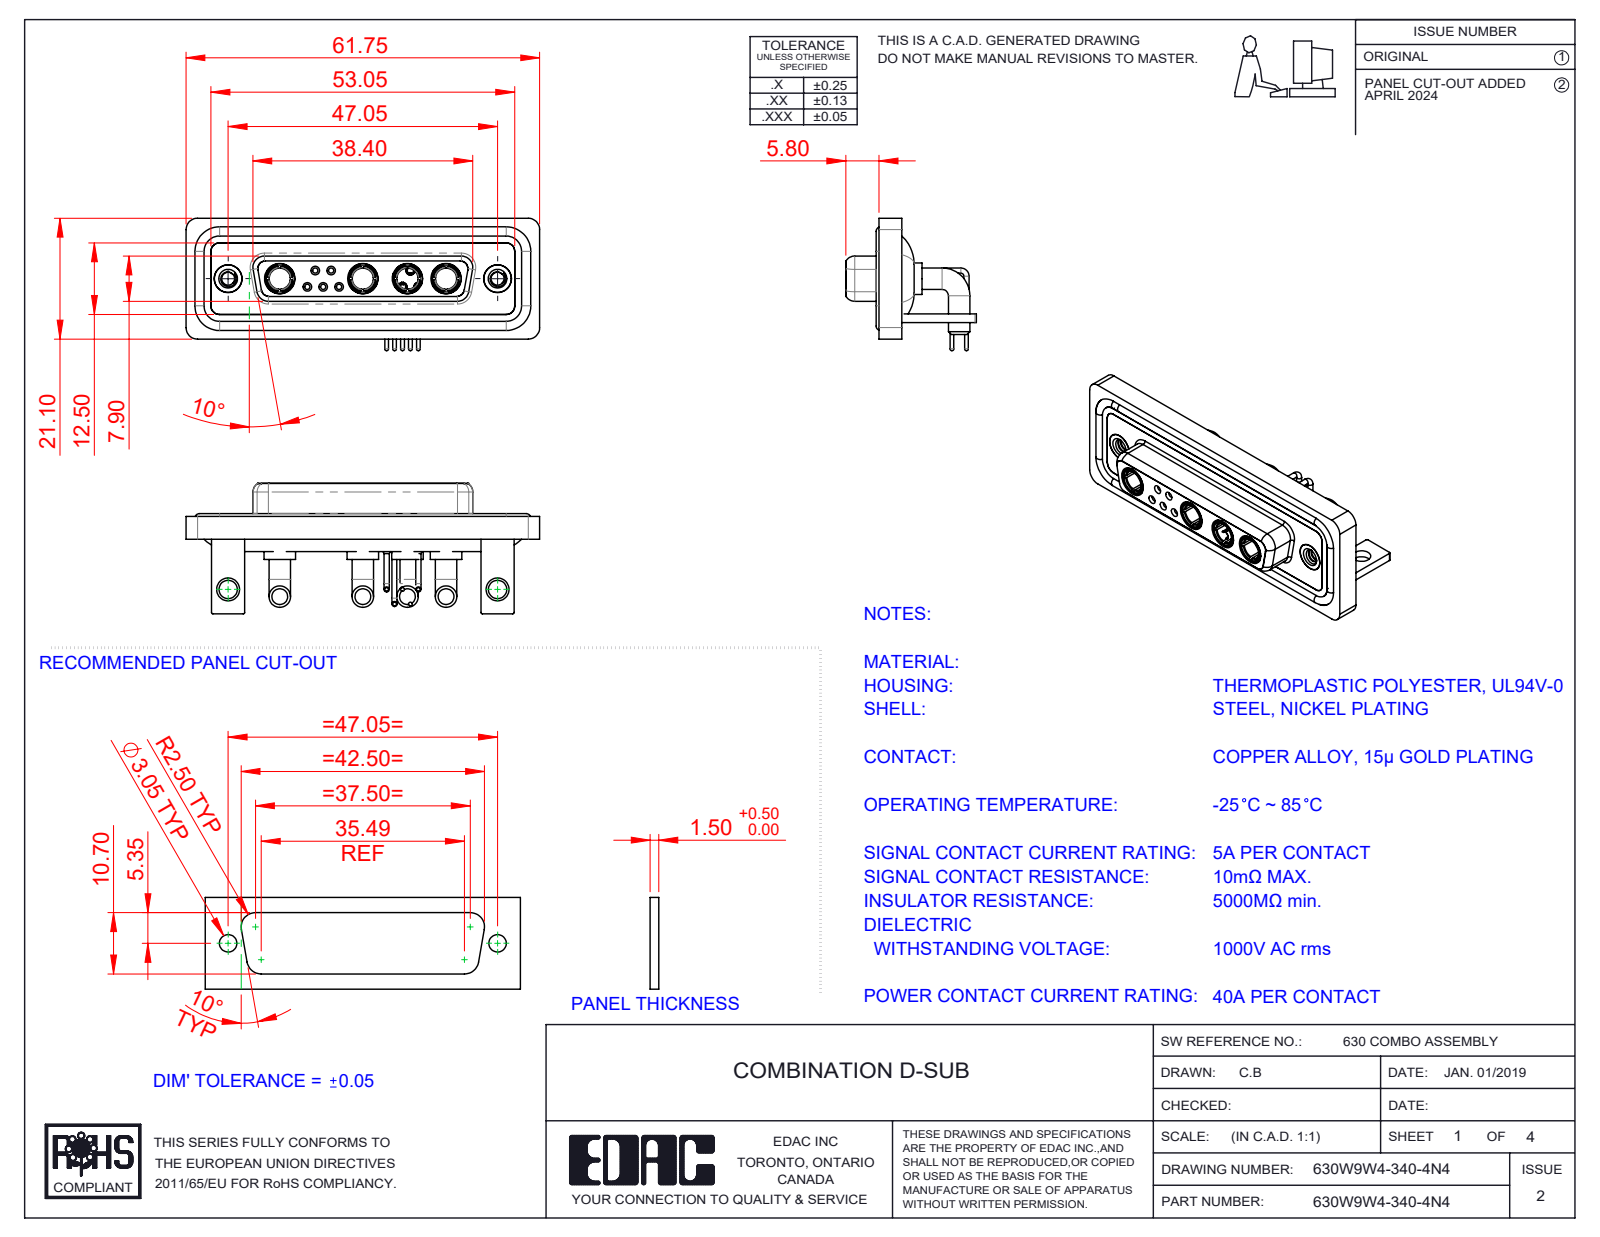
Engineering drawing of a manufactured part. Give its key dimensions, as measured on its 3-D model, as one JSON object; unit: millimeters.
{"part_name": "630Combo Waterproof Housing_25 Contacts; 630Combo Shell Rear_25 Contacts; Power Socket_40A RA; 630Combo Shell Front_25 Contacts (+6 more)", "step_written_by": "SolidWorks 2023 (CONFIG_CONTROL_DESIGN)", "units": "millimeters", "bodies": {"solids": 22, "faces": 1011, "planar": 316, "cylindrical": 427, "other": 268}, "overall_size": [61.75, 23.12, 22.8], "volume_mm3": 9109, "surface_area_mm2": 14957, "round_holes": [[4.85, 6], [0.9, 5], [1.1, 5], [1.5, 5], [2, 5], [3.7, 4], [5.3, 4], [1.6, 3], [1.7, 2], [2.26, 2], [3.2, 2], [4, 2]], "round_bosses_or_shafts": [[0.9, 10], [1.6, 9], [3.75, 8], [2, 5], [1.5, 5], [0.65, 5], [5.5, 4], [5.2, 4]], "partial_cylinders_radius": [[2, 19], [1.5, 18], [0.25, 16], [1.35, 8], [1.6, 8], [0.5, 5], [0.6, 4], [0.65, 4]], "face_to_face_distances": [0.4, 1.8, 2.9, 3.7, 1.5, 4.1, 1.1, 1.4, 1.6, 2.5], "hole_center_spacings": [3.16, 2.77, 5.04, 13.85, 11.08, 12.79, 15.5, 5.54]}
